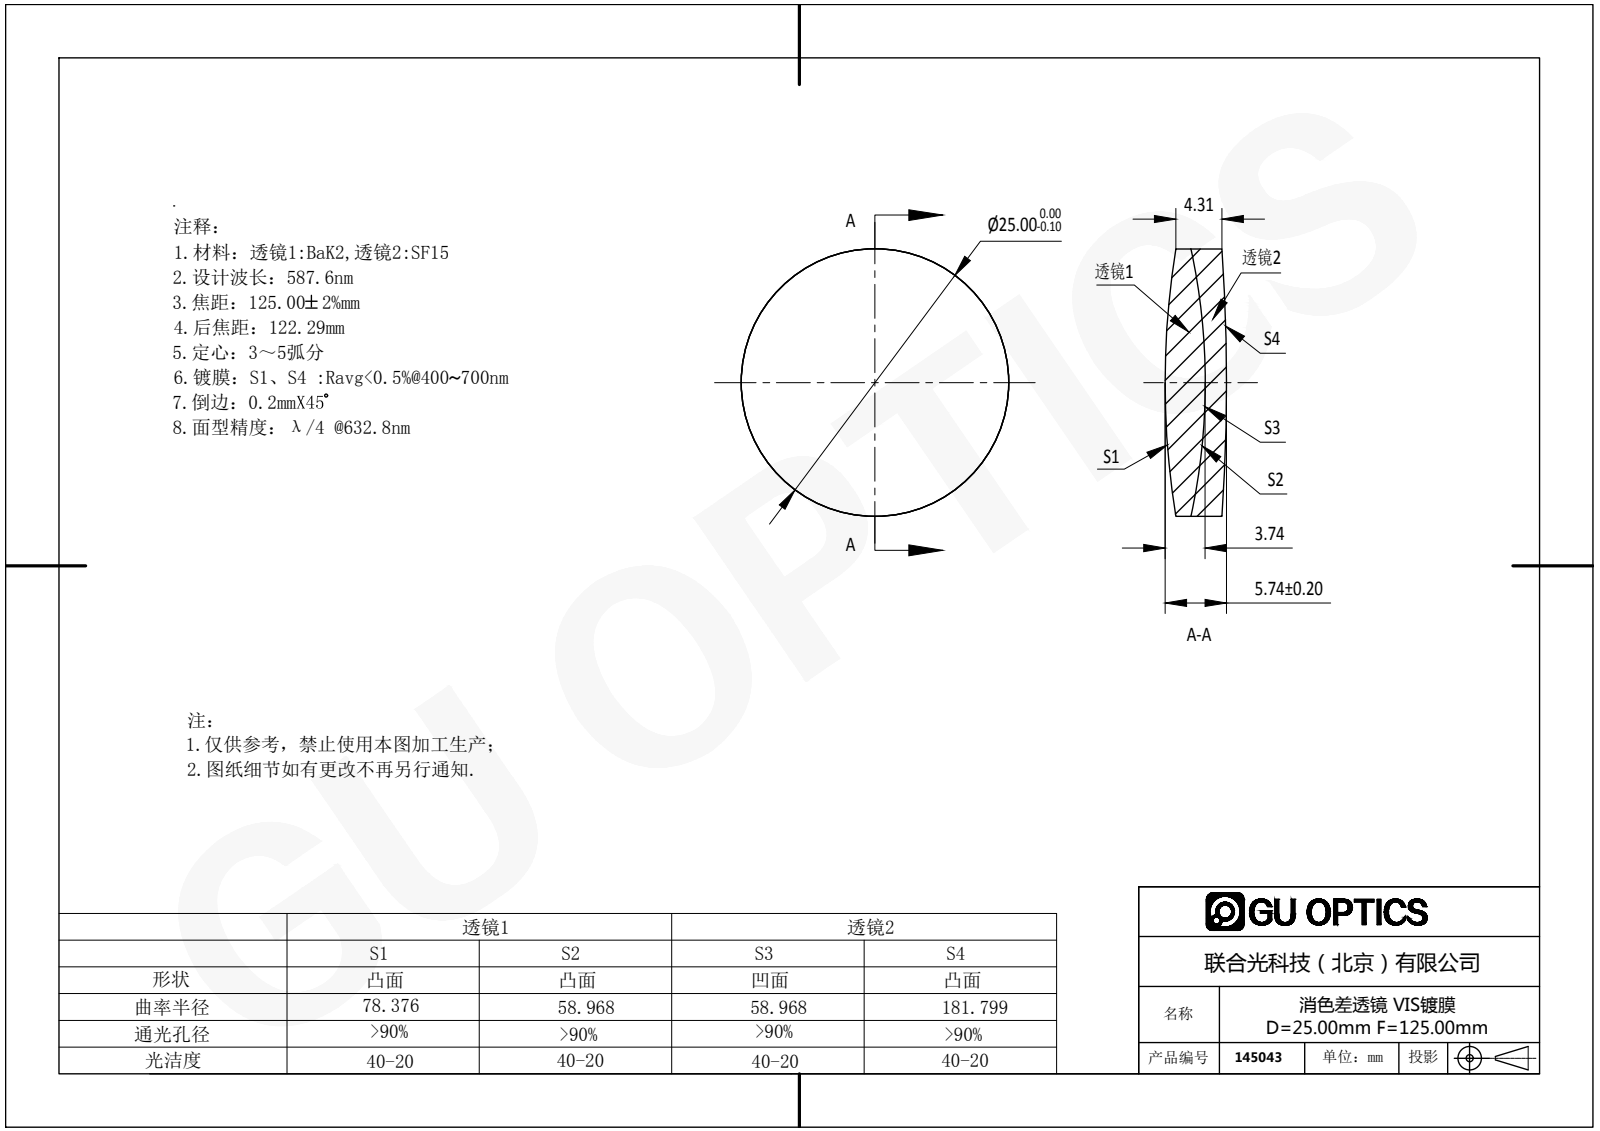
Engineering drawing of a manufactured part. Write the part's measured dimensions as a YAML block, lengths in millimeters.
part_name: "145043"
step_written_by: "SolidWorks 2016 (AUTOMOTIVE_DESIGN)"
units: millimeters
bodies: {solids: 2, faces: 12, planar: 0, cylindrical: 4, other: 8}
overall_size: [25, 25, 5.74]
volume: 2466
surface_area: 2317
round_bosses_or_shafts:
  - {diameter: 25, count: 1}
